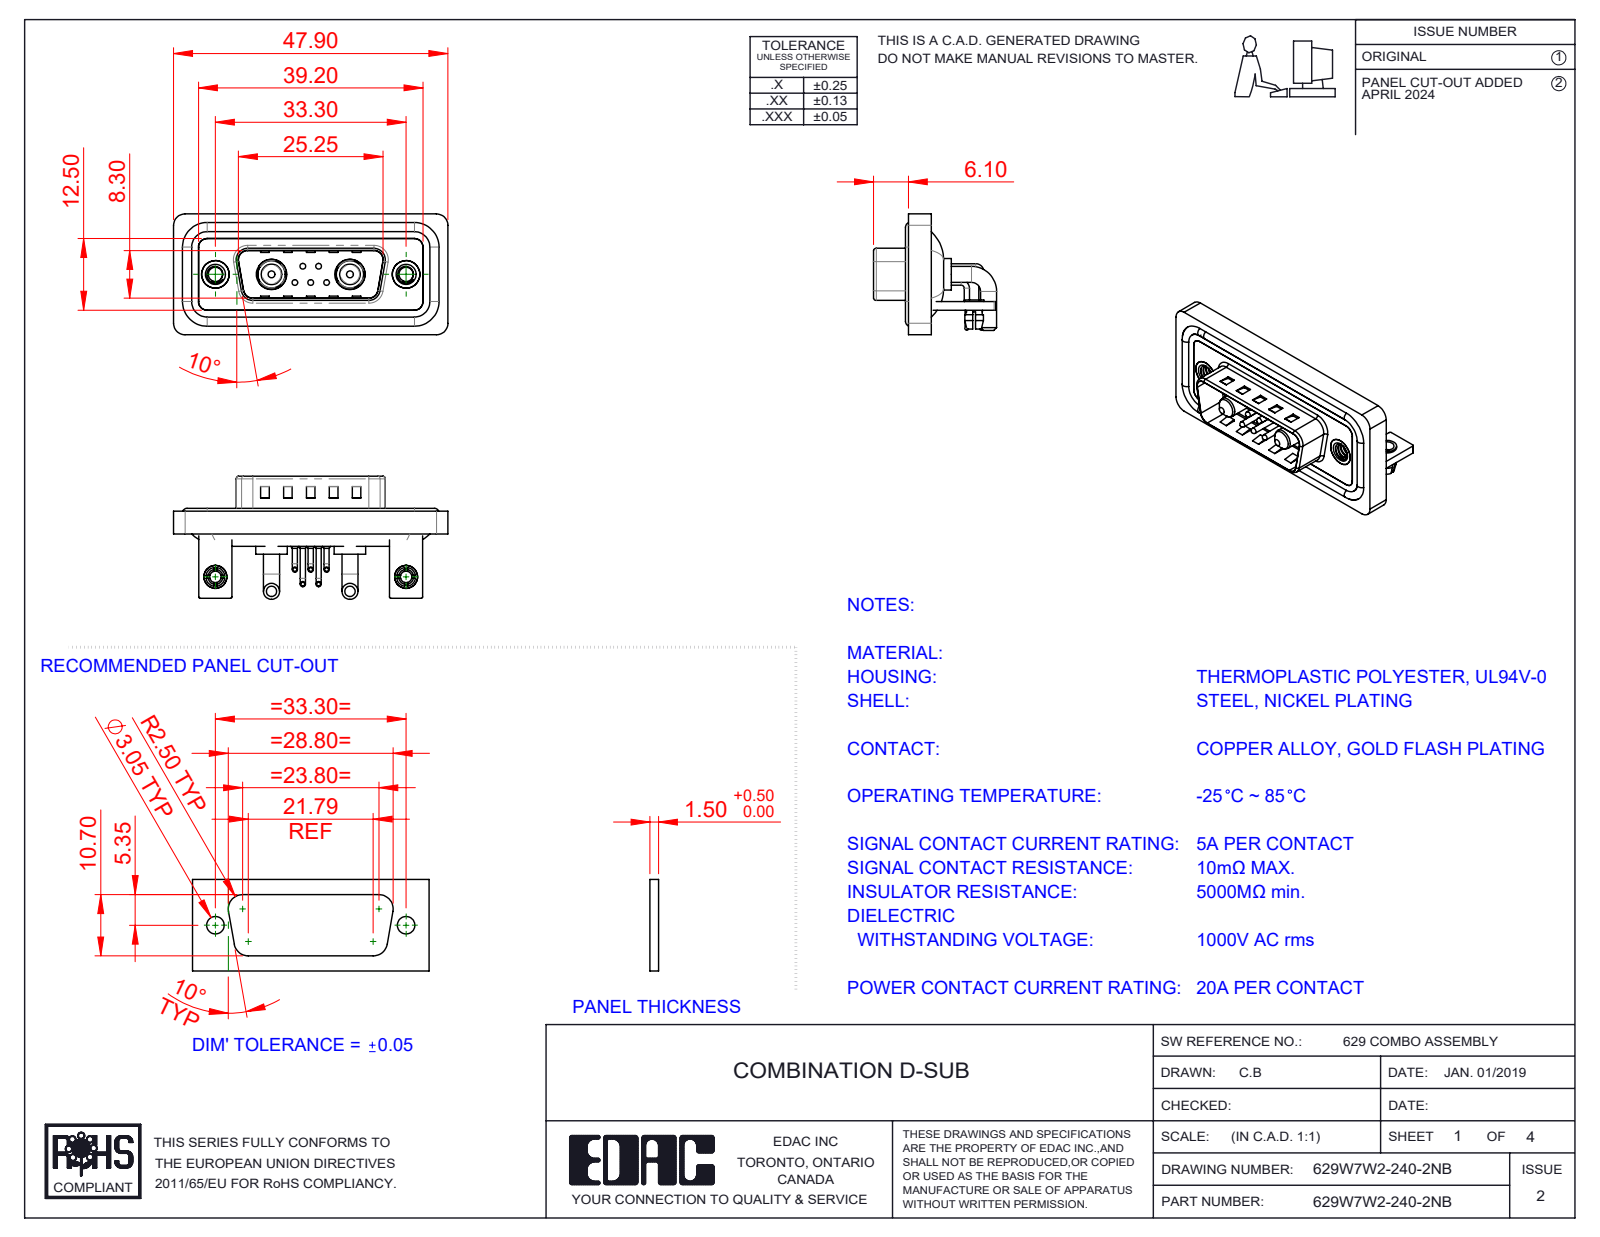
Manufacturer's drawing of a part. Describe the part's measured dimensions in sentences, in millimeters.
The part is named "629Combo Shell Front_15 Contacts; Power Pin_20A RA; 629W7W2-140-2NB; 629Combo Waterproof Housing_15 Contacts (+7 more)". Its 3-D file was written by "SolidWorks 2023 (CONFIG_CONTROL_DESIGN)". It is 20 solids with 1213 faces: 585 planar, 456 cylindrical and 172 other. Overall it measures 47.9 by 21.5 by 21.1 millimeters. Its volume is 5 989 cubic millimeters and its surface area 9 939 square millimeters. Round holes: 7 of diameter 2, 5 of diameter 0.75, 5 of diameter 1.6, 4 of diameter 2.5, 2 of diameter 3.2, 2 of diameter 4, 2 of diameter 4.8, 2 of diameter 4.85, 2 of diameter 5, 2 of diameter 5.3. Round bosses or shafts: 10 of diameter 0.9, 5 of diameter 1.5, 5 of diameter 1, 5 of diameter 0.65, 4 of diameter 2.8, 4 of diameter 1.6, 2 of diameter 5.5, 2 of diameter 5.2. Partial cylindrical surfaces (rounded edges, fillets, slot ends): 21 of radius 2, 18 of radius 1.5, 16 of radius 0.25, 9 of radius 0.5, 8 of radius 1.6, 5 of radius 1.01, 4 of radius 0.6, 4 of radius 0.65. The main face-to-face distances are 0.4, 1.5, 0.8, 2.9, 2.1, 1.1, 1.6, 1.2, 3.7, 4.5. The hole center spacings are 3.16, 2.77, 9.8, 23.5, 33.3, 4.31, 4.33, 5.03.
